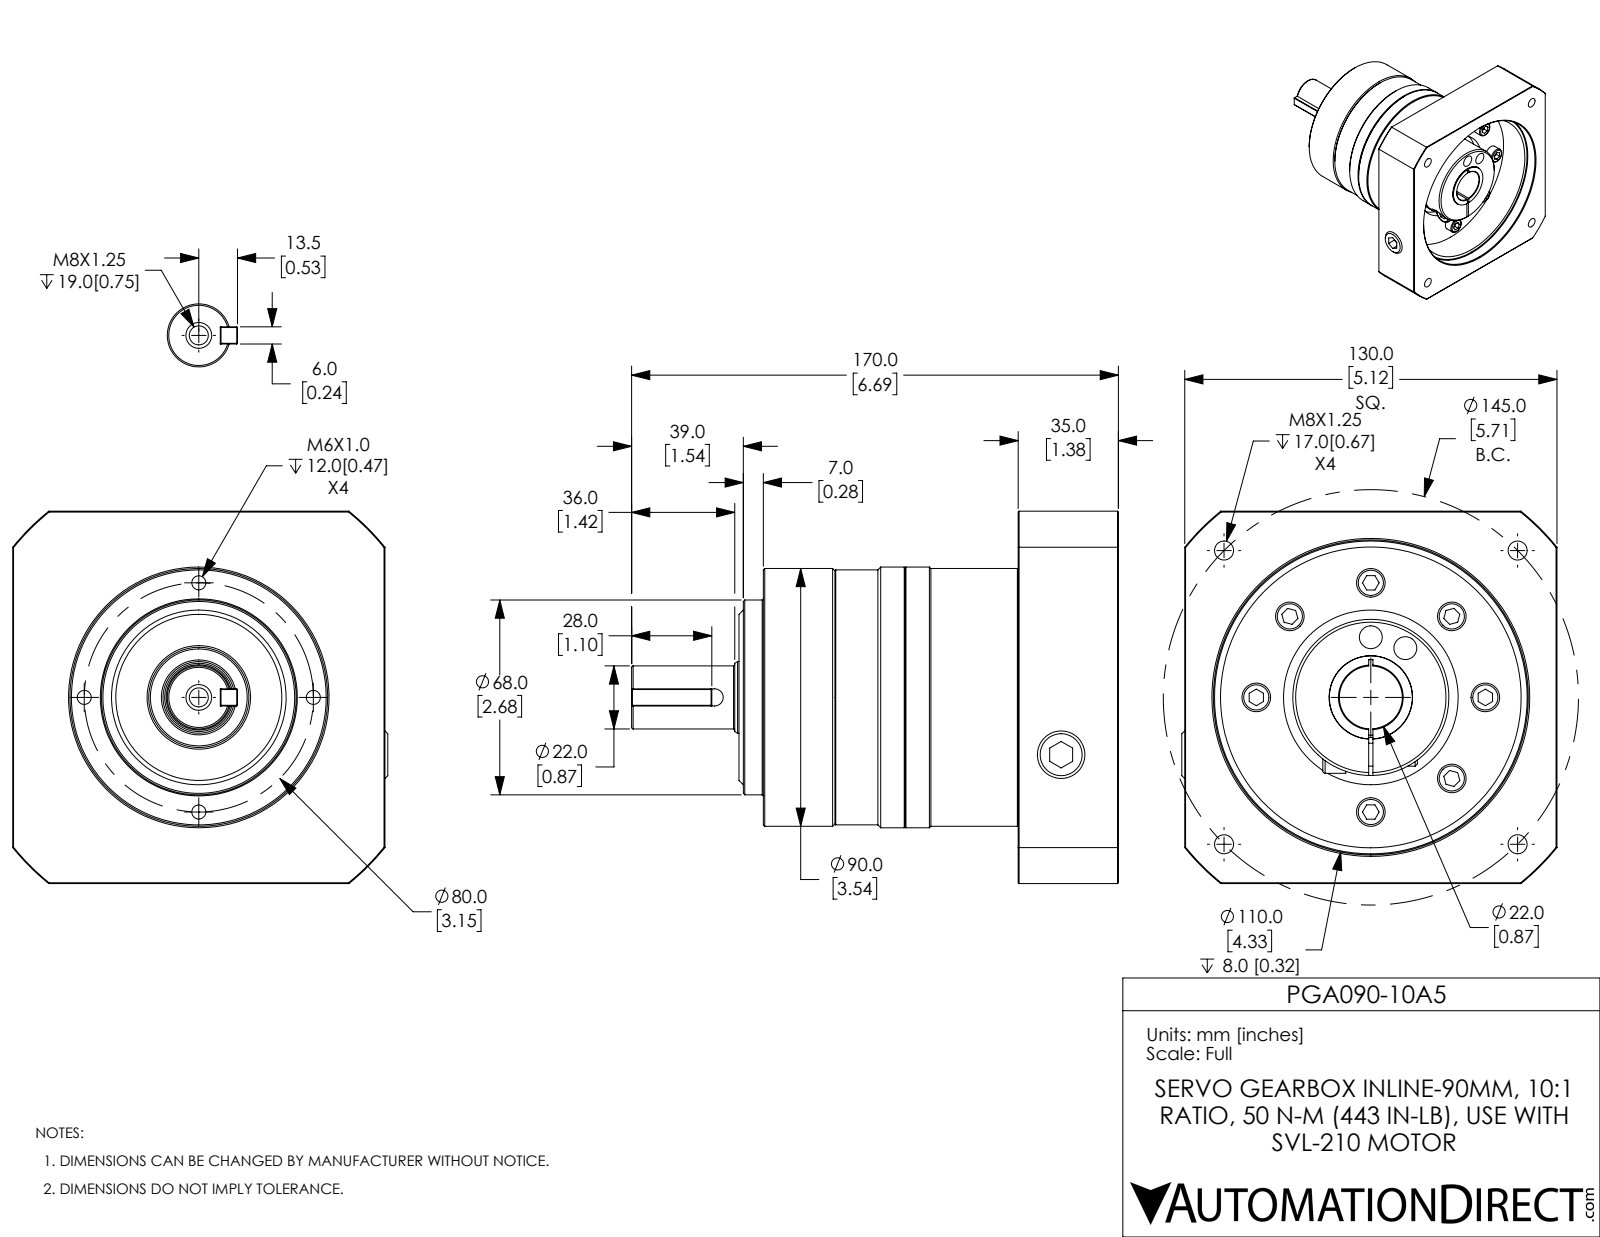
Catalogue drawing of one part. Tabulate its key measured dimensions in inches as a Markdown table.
| quantity | value |
| --- | --- |
| part name | PGA090-10A5 |
| STEP written by | SolidWorks 2019 (CONFIG_CONTROL_DESIGN) |
| units | inches |
| bodies | 1 solid, 345 faces (136 planar, 87 cylindrical, 122 other) |
| overall size | 6.693 × 5.157 × 5.118 |
| volume | 57.13 in³ |
| surface area | 169.3 in² |
| round holes (diameter × count) | 0.262 × 5, 0.194 × 4, 0.315 × 2, 0.346 × 1, 0.561 × 1, 0.866 × 1, 2.402 × 1, 4.134 × 1, 4.331 × 1 |
| round bosses / shafts (diameter × count) | 0.394 × 7, 3.583 × 1, 3.543 × 1, 3.504 × 1, 2.677 × 1, 2.146 × 1, 1.142 × 1, 1.102 × 1 |
| partial cylindrical surfaces (radius × count) | 0.118 × 1, 0.131 × 1, 0.276 × 1, 3.287 × 1 |
| main face-to-face distances | 5.118, 1.378, 0.236, 1.142, 3.504, 4.882, 3.74, 0.059, 4.075, 5.217 |
| hole center spacings | 2.067, 4.121, 1.575, 2.227, 2.855, 4.037, 0.827, 1.779 |
